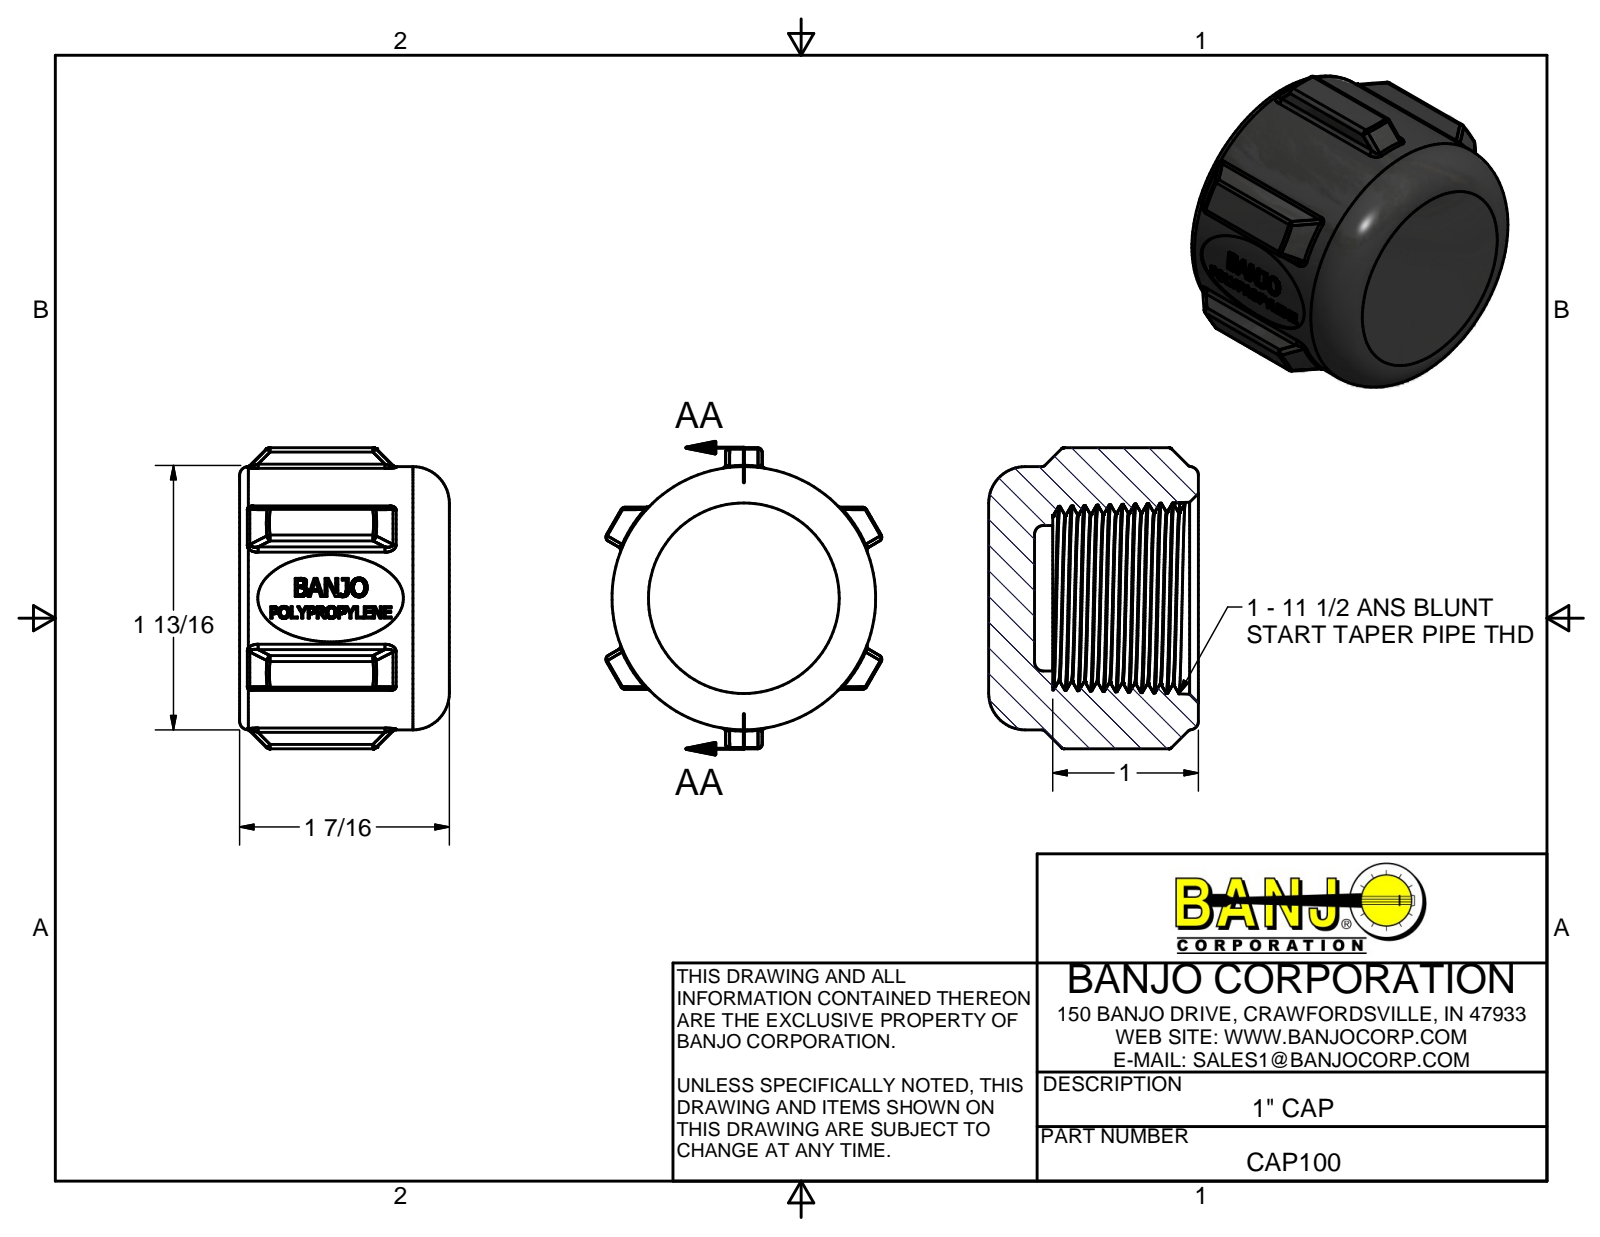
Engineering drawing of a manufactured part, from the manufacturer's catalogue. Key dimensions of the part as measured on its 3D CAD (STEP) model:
Part name (STEP PRODUCT): CAP100
STEP written by: Autodesk Inventor 2013 (AUTOMOTIVE_DESIGN)
Units: inches
Bodies: 1 solid, 448 faces (160 planar, 55 cylindrical, 233 other)
Overall size (bounding box): 2.07 × 1.896 × 1.44
Volume: 2.508 in³ · Surface area: 20.52 in²
Round holes (diameter × count): ⌀1 ×1
Round bosses / shafts (diameter × count): ⌀1.81 ×1
Partial cylindrical surfaces — rounded edges, fillets, slot ends (radius × count): R0.03 ×24, R0.895 ×1
Main face-to-face distances: 1.44, 0.315, 1.125, 2.07, 0.125, 1, 0.44, 0.409, 1.661, 0.25
